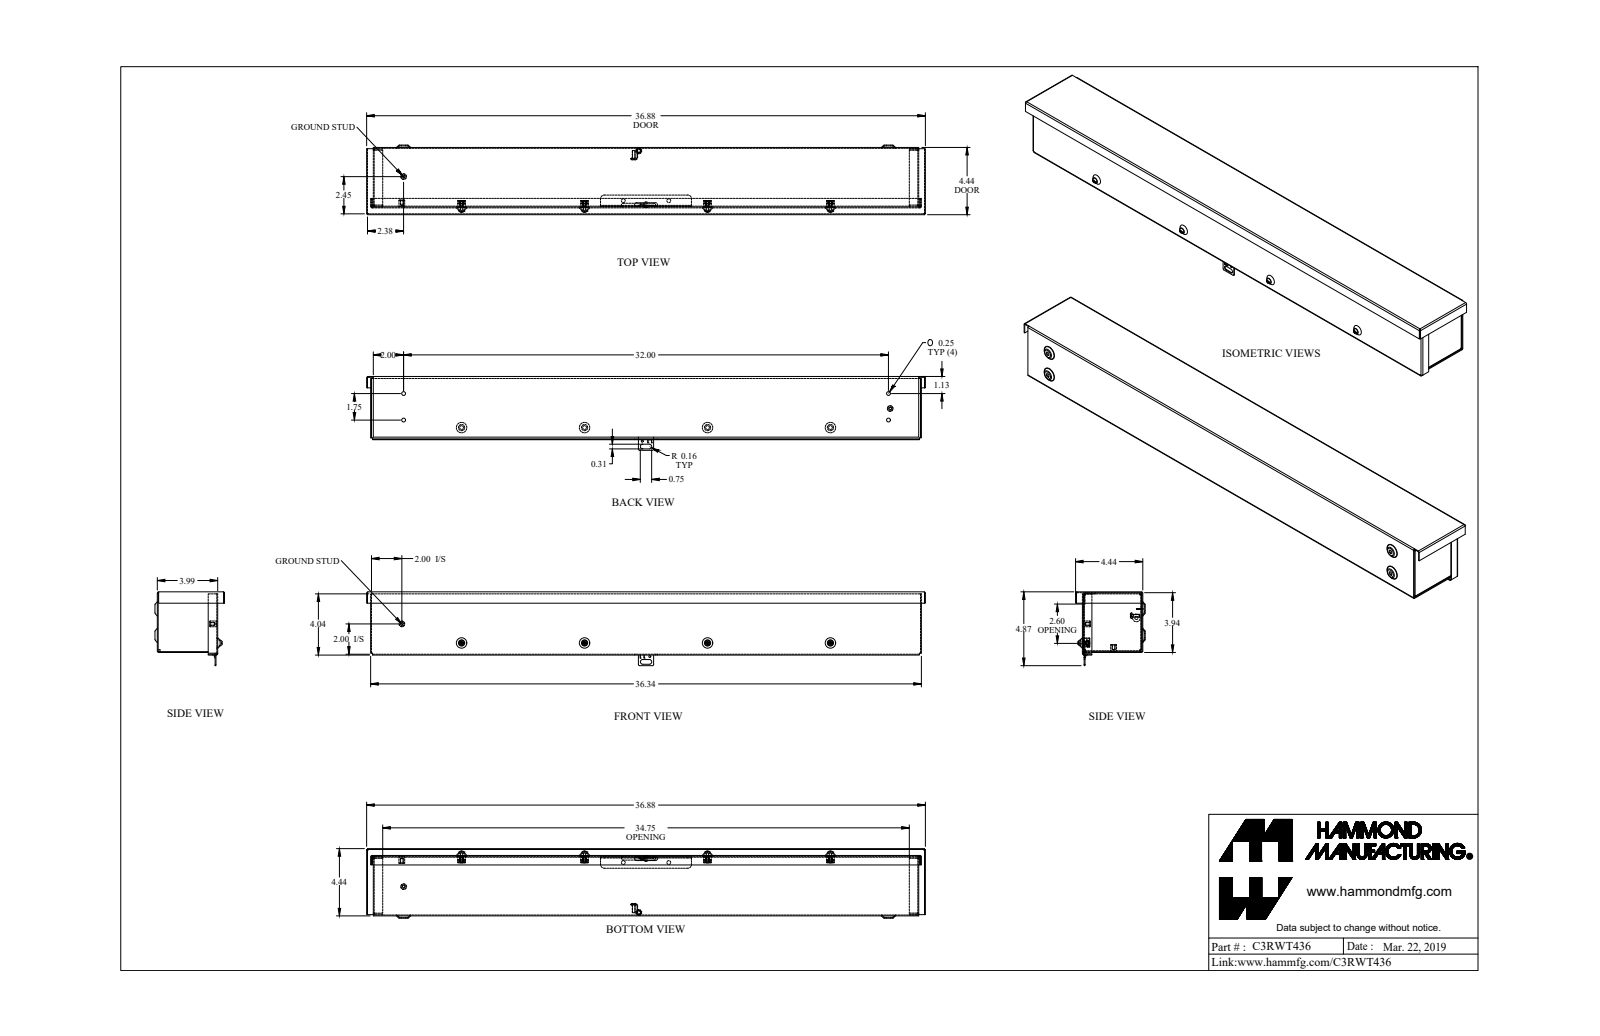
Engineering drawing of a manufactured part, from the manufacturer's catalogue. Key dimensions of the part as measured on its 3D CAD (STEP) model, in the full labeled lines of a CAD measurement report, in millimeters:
Part name (STEP PRODUCT): C3RWT436_Default
STEP written by: SolidWorks 2019 (CONFIG_CONTROL_DESIGN)
Units: millimetres
Bodies: 25 solids, 887 faces (486 planar, 277 cylindrical, 124 other)
Overall size (bounding box): 936.6 × 123.7 × 116.7
Volume: 689 900 mm³ · Surface area: 961 900 mm²
Round holes (diameter × count): ⌀4 ×6, ⌀6.4 ×6, ⌀5.4 ×4, ⌀5.8 ×4, ⌀5.2 ×2, ⌀3.2 ×1, ⌀3.5 ×1, ⌀5.1 ×1, ⌀5.5 ×1
Round bosses / shafts (diameter × count): ⌀4.8 ×5, ⌀3.8 ×4, ⌀9.5 ×2, ⌀12.7 ×1, ⌀9.3 ×1, ⌀5.3 ×1, ⌀3.9 ×1, ⌀3.2 ×1
Partial cylindrical surfaces — rounded edges, fillets, slot ends (radius × count): R0.7 ×18, R2.2 ×18, R2 ×16, R2.7 ×16, R3.2 ×14, R0.6 ×8, R6.4 ×6, R0.4 ×4
Main face-to-face distances: 1.4, 100.2, 99.8, 98.3, 98.7, 101.2, 101.6, 111.3, 13, 11.5
Hole centre spacings: 206.1, 412.2, 103.1, 206.1, 241.5, 271.2, 303.6, 308.7
